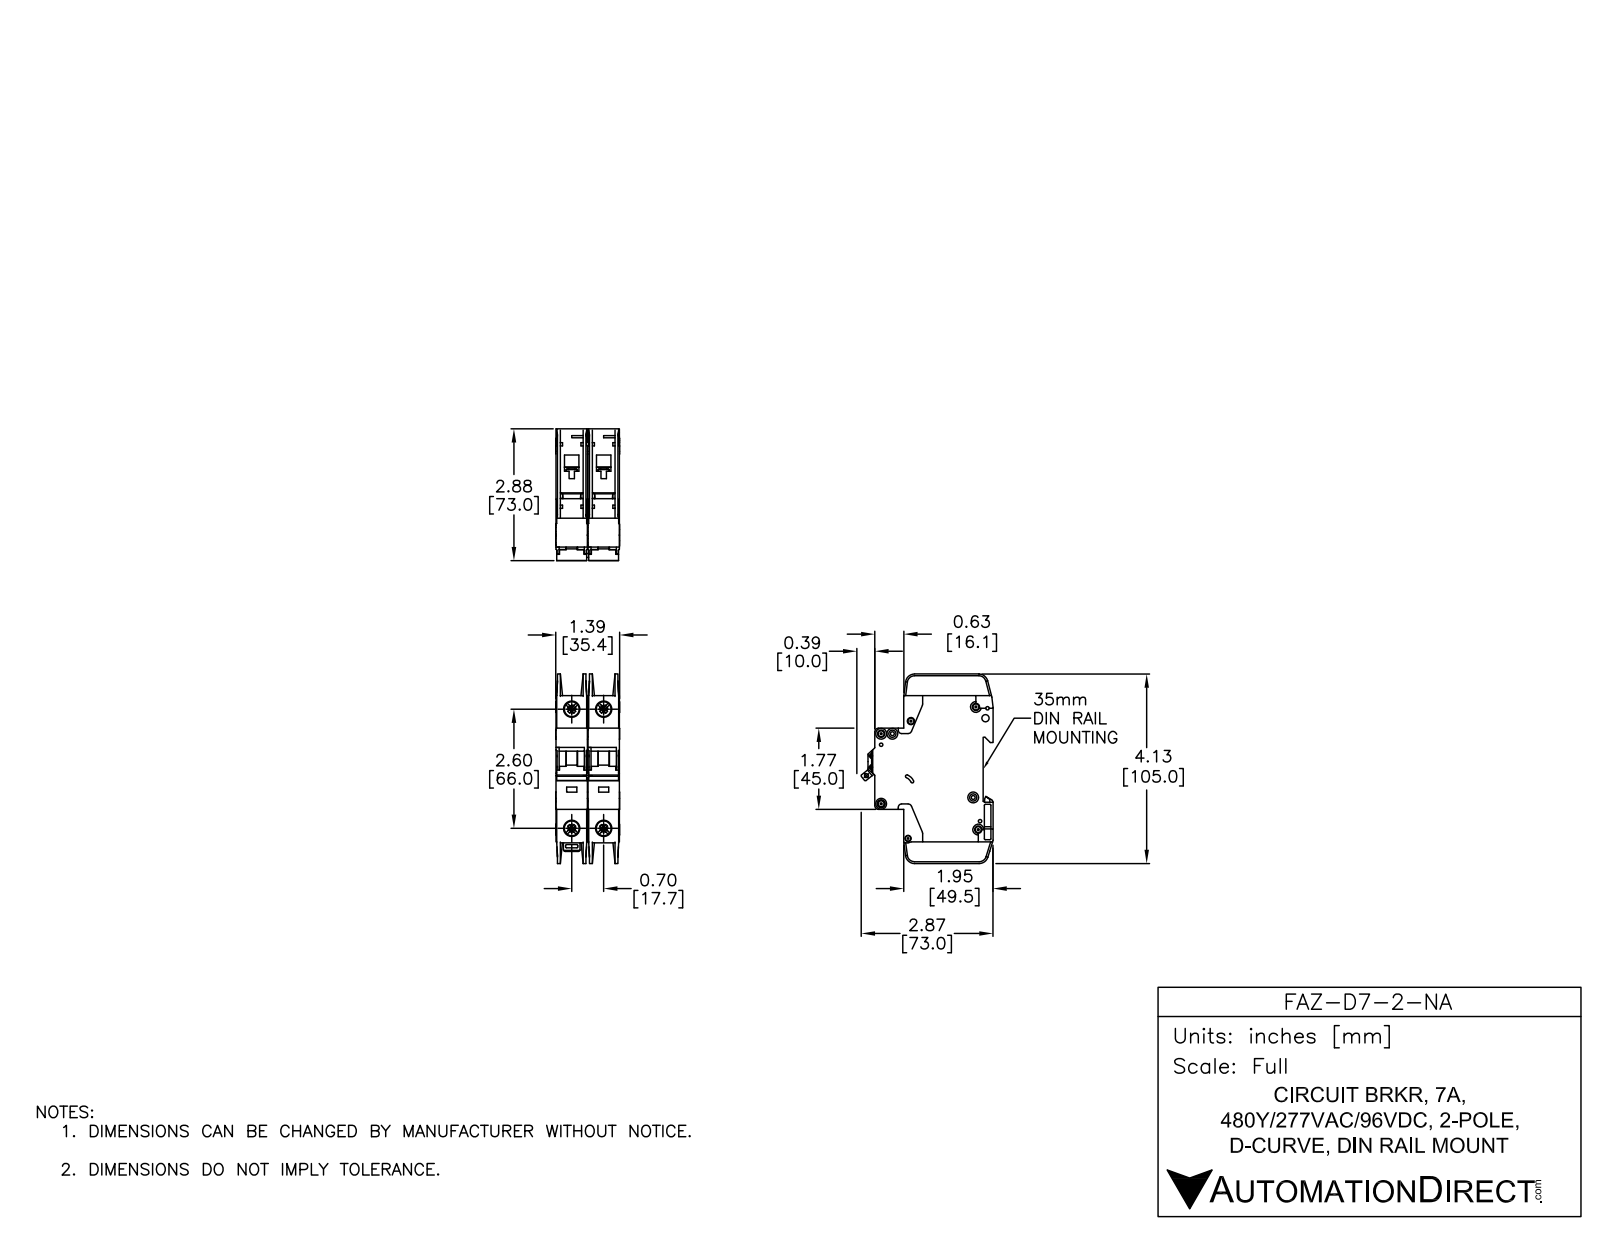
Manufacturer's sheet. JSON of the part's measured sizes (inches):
{"part_name": "FAZ-D7-2-NA", "step_written_by": "SolidWorks 2014 (AUTOMOTIVE_DESIGN)", "units": "inches", "bodies": {"solids": 6, "faces": 1568, "planar": 818, "cylindrical": 526, "other": 224}, "overall_size": [4.134, 2.876, 1.394], "volume_in3": 9.482, "surface_area_in2": 76.69, "round_holes": [[0.142, 7], [0.281, 4], [0.323, 4], [0.043, 2], [0.059, 2], [0.157, 2], [0.075, 1], [0.085, 1], [0.087, 1], [0.1, 1], [0.13, 1], [0.134, 1]], "round_bosses_or_shafts": [[0.236, 7], [0.098, 2]], "partial_cylinders_radius": [[0.01, 47], [0.02, 24], [0.039, 18], [0.079, 12], [0.197, 5], [0.071, 4], [0.157, 4], [0.008, 2]], "face_to_face_distances": [0.697, 0.689, 0.028, 0.593, 0.096, 0.069, 0.62, 0.524, 1.386, 0.669], "hole_center_spacings": [0.244, 0.697, 2.598, 2.69, 0.204, 0.24, 0.322, 0.337]}
